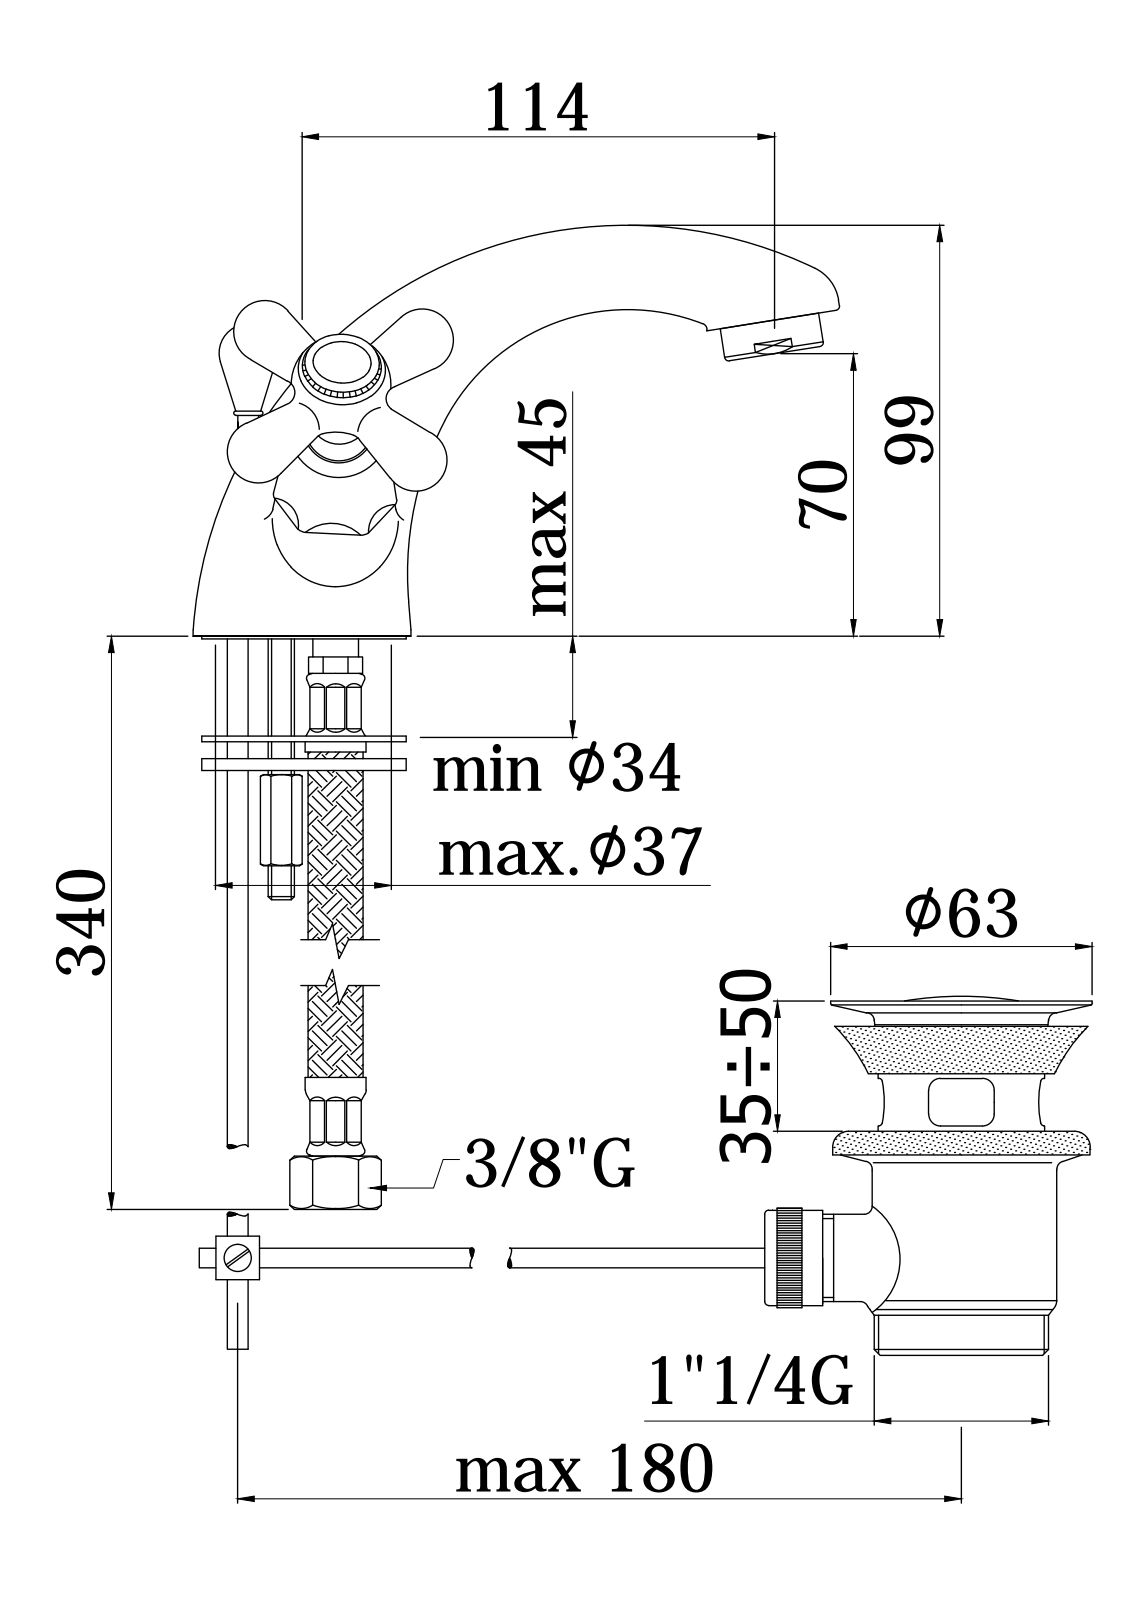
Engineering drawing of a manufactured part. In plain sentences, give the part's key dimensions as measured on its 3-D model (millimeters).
The part is named "IRV075CR". Its 3-D file was written by "CREO PARAMETRIC BY PTC INC, 2020044 (CONFIG_CONTROL_DESIGN)". It is 3 solids with 295 faces: 62 planar, 64 cylindrical and 169 other. Overall it measures 188.47 by 156.55 by 98.4 millimeters. Its volume is 254 858 cubic millimeters and its surface area 49 352 square millimeters. Round holes: 3 of diameter 5.5, 2 of diameter 7.75, 2 of diameter 8, 2 of diameter 9, 2 of diameter 11, 2 of diameter 18.6, 2 of diameter 21.5, 1 of diameter 42.5. Round bosses or shafts: 2 of diameter 27.5, 2 of diameter 18, 2 of diameter 13.5, 1 of diameter 37.5, 1 of diameter 24, 1 of diameter 5. Partial cylindrical surfaces (rounded edges, fillets, slot ends): 2 of radius 14.5. The main face-to-face distances are 26.5, 21.9, 7.7, 24.1, 46, 2, 22, 24, 26, 1.9. The hole center spacings are 10.97, 12.08, 13.46, 13.6, 22.3, 22.61, 13, 15.
